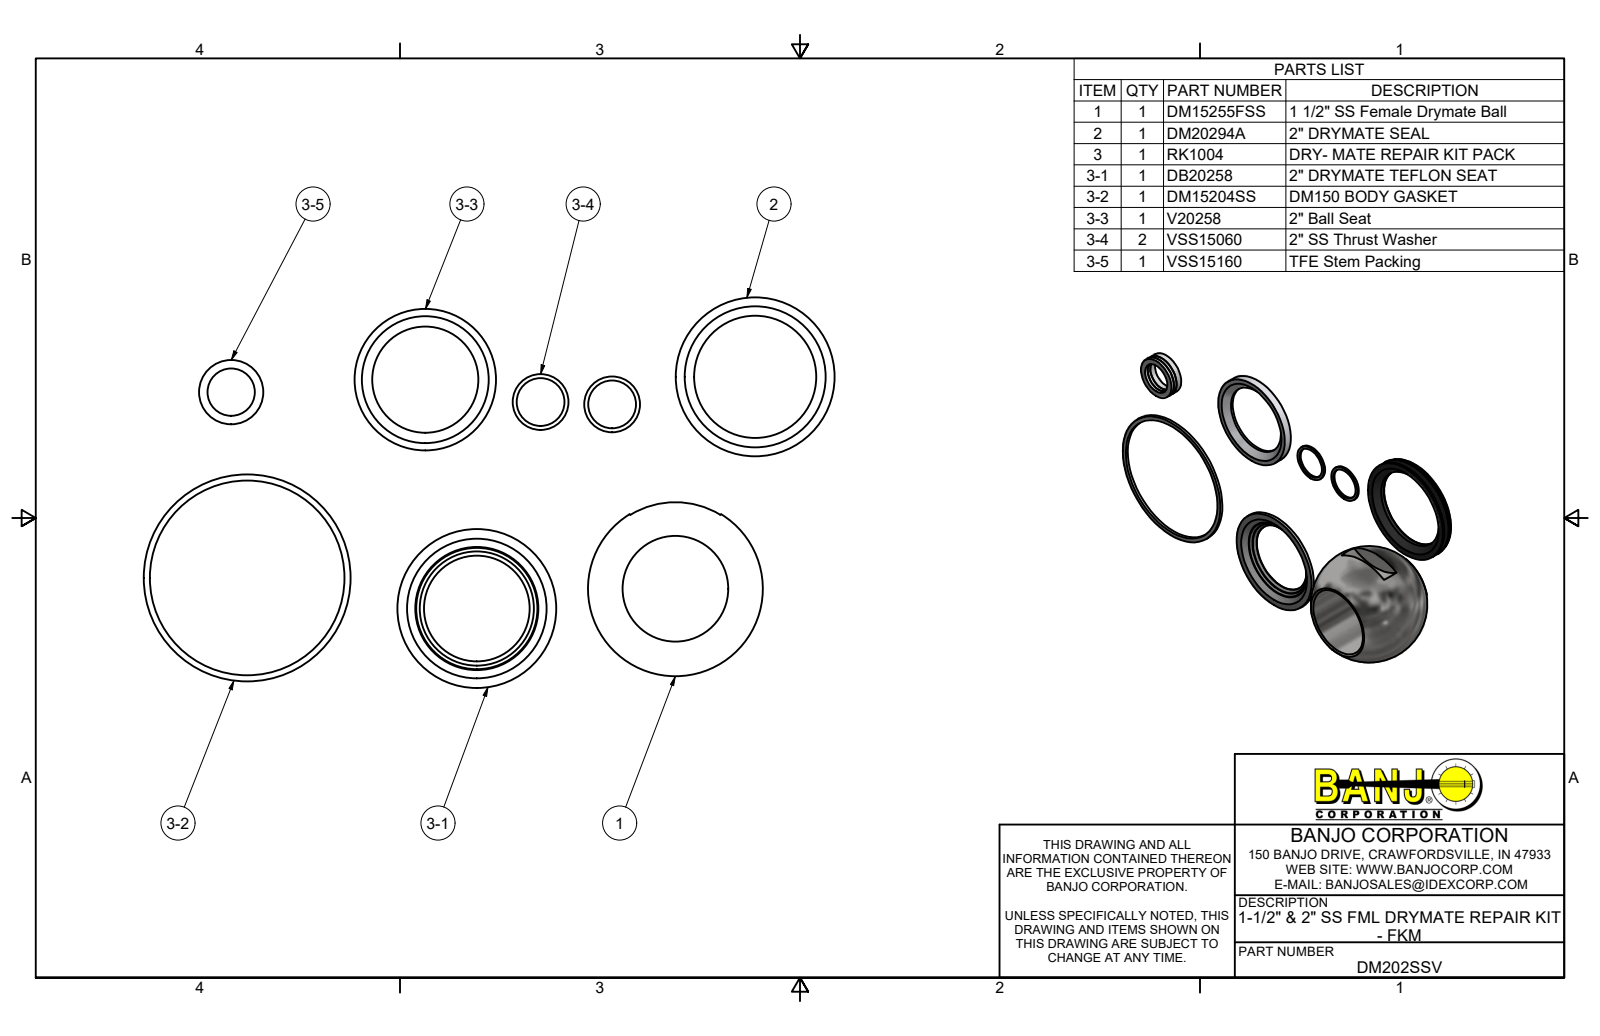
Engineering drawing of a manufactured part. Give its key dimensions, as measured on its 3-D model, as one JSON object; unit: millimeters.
{"part_name": "DM202SSV; RK1004; DB20258; DM15204SS (+8 more)", "step_written_by": "Autodesk Inventor 2019 (AUTOMOTIVE_DESIGN)", "units": "millimeters", "bodies": {"solids": 10, "faces": 82, "planar": 28, "cylindrical": 23, "other": 31}, "overall_size": [248.6, 140.4, 48.5], "volume_mm3": 76940, "surface_area_mm2": 32880, "round_holes": [[38.1, 3], [17.2, 2], [17, 1], [41, 1], [43.9, 1], [54.6, 1], [70, 1]], "round_bosses_or_shafts": [[57.2, 2], [20.1, 2], [74.5, 1], [50.8, 1], [23.2, 1]], "partial_cylinders_radius": [[30, 1]], "face_to_face_distances": [1.5, 6, 4.4, 4.3, 5.8, 0.9, 1.3, 4.6, 3.1, 1.2], "hole_center_spacings": [25.8, 42.3, 52.4, 67, 67.8, 70, 70.1, 71.8]}
